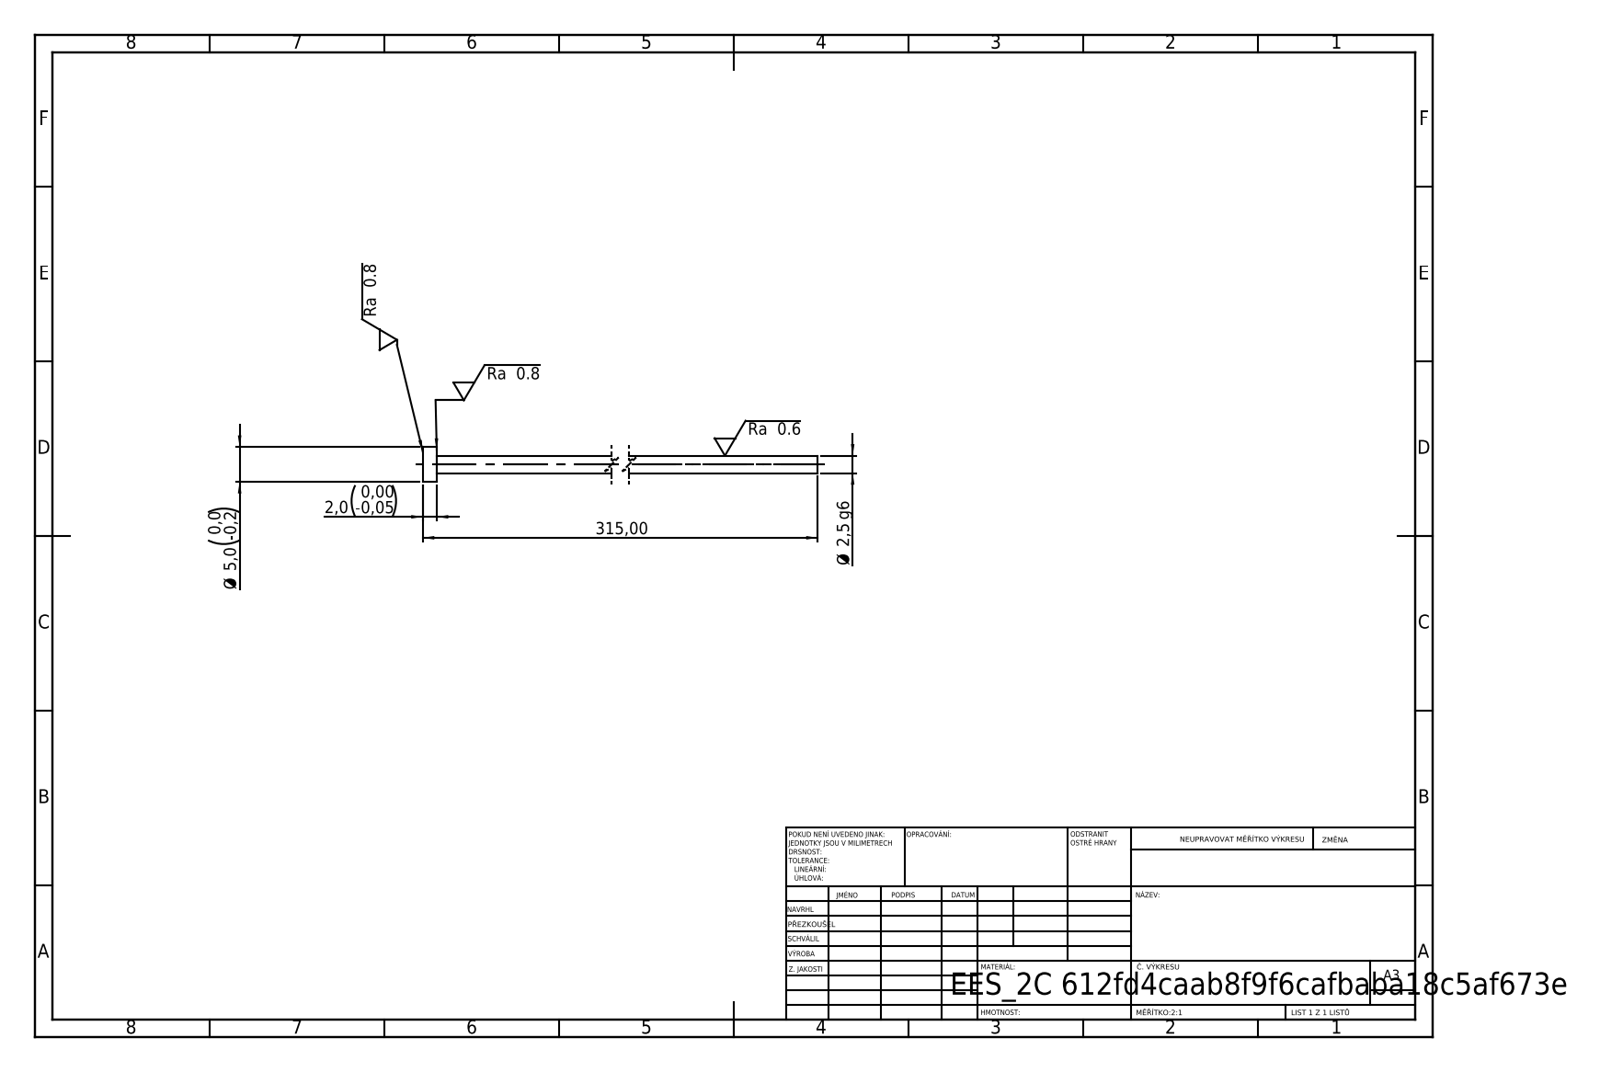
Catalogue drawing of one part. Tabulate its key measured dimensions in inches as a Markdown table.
| quantity | value |
| --- | --- |
| STEP written by | SolidWorks 2019 (CONFIG_CONTROL_DESIGN) |
| units | inches |
| bodies | 1 solid, 7 faces (3 planar, 4 cylindrical, 0 other) |
| overall size | 12.402 × 0.197 × 0.197 |
| volume | 0.096 in³ |
| surface area | 3.92 in² |
| round bosses / shafts (diameter × count) | 0.197 × 1, 0.098 × 1 |
| main face-to-face distances | 0.079, 12.402, 12.323 |
